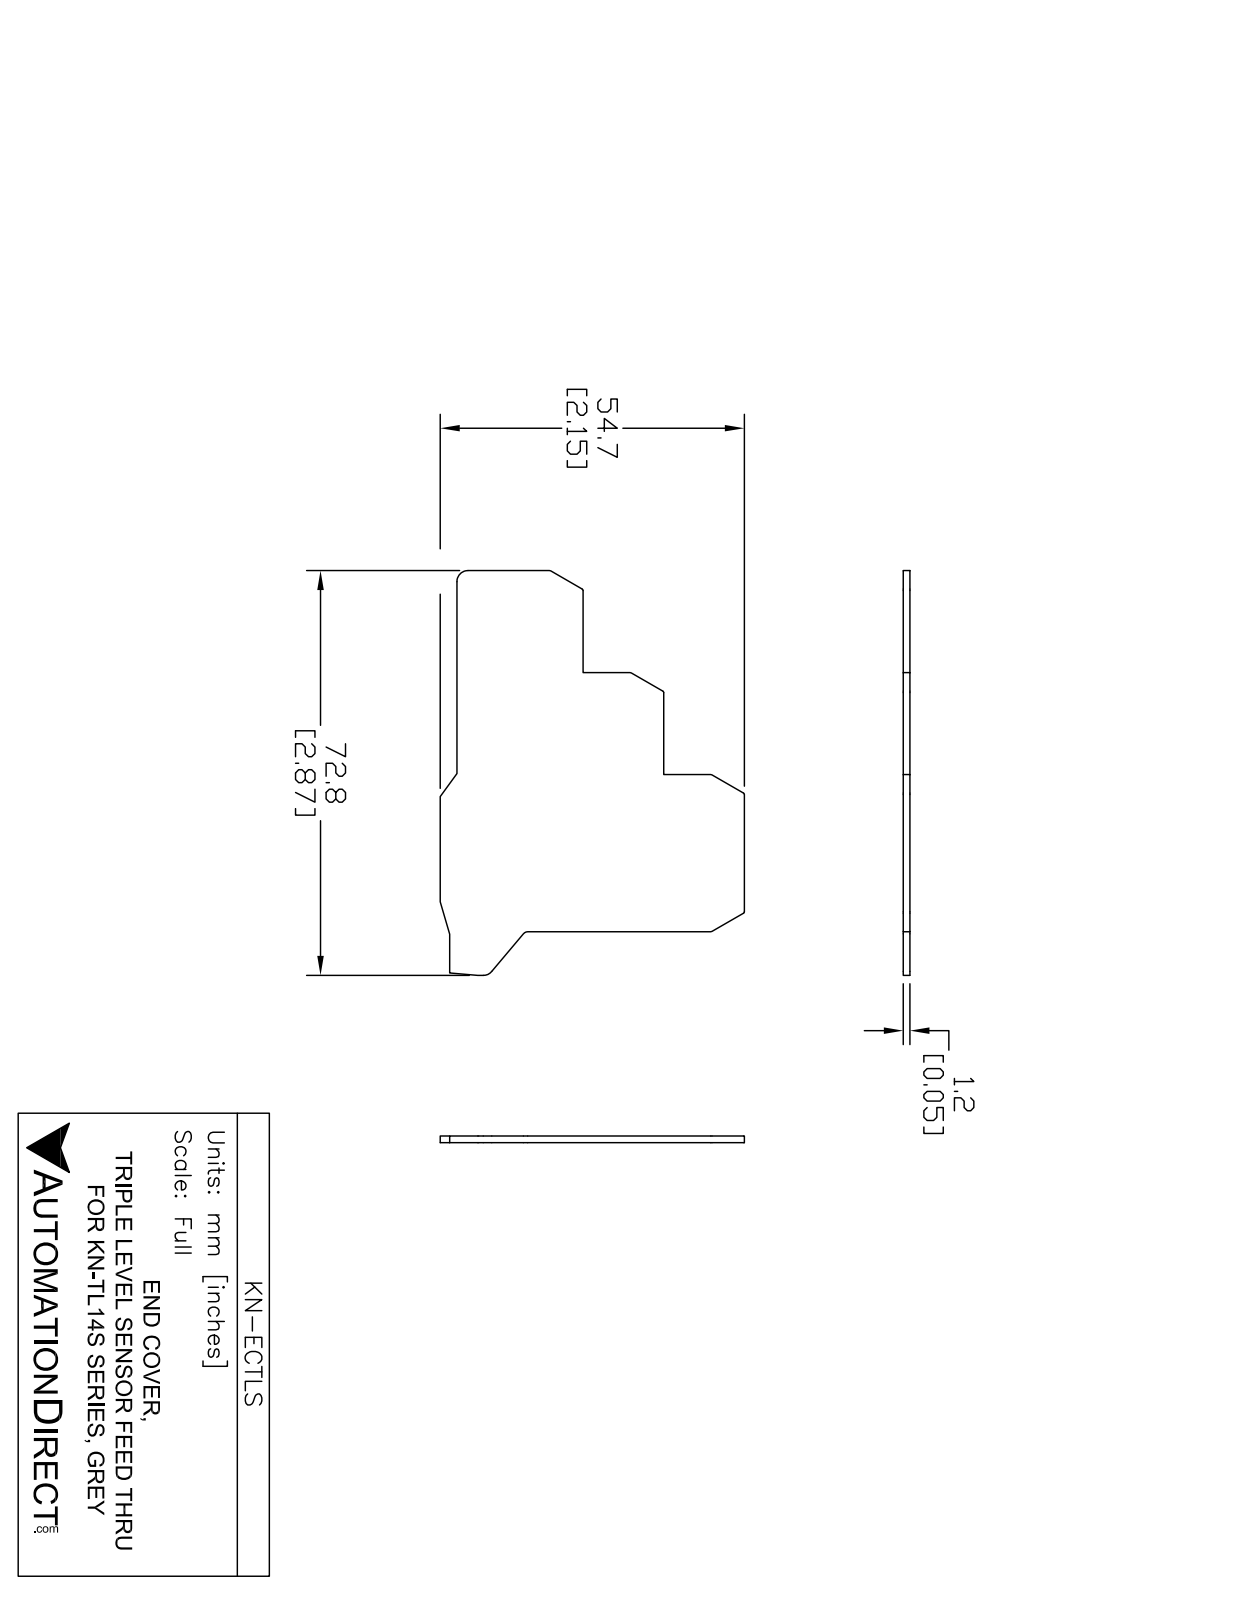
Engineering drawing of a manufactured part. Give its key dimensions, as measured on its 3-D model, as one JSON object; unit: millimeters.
{"part_name": "KN-ECTLS", "step_written_by": "SolidWorks 2014 (AUTOMOTIVE_DESIGN)", "units": "millimeters", "bodies": {"solids": 1, "faces": 33, "planar": 21, "cylindrical": 12, "other": 0}, "overall_size": [72.85, 54.7, 1.2], "volume_mm3": 3210, "surface_area_mm2": 5633, "partial_cylinders_radius": [[0.3, 4], [0.5, 4], [2, 3], [1, 1]], "face_to_face_distances": [1.2, 14.5, 51.7, 3, 54.7, 18.35, 40.2, 37.2, 25.7, 22.7]}
